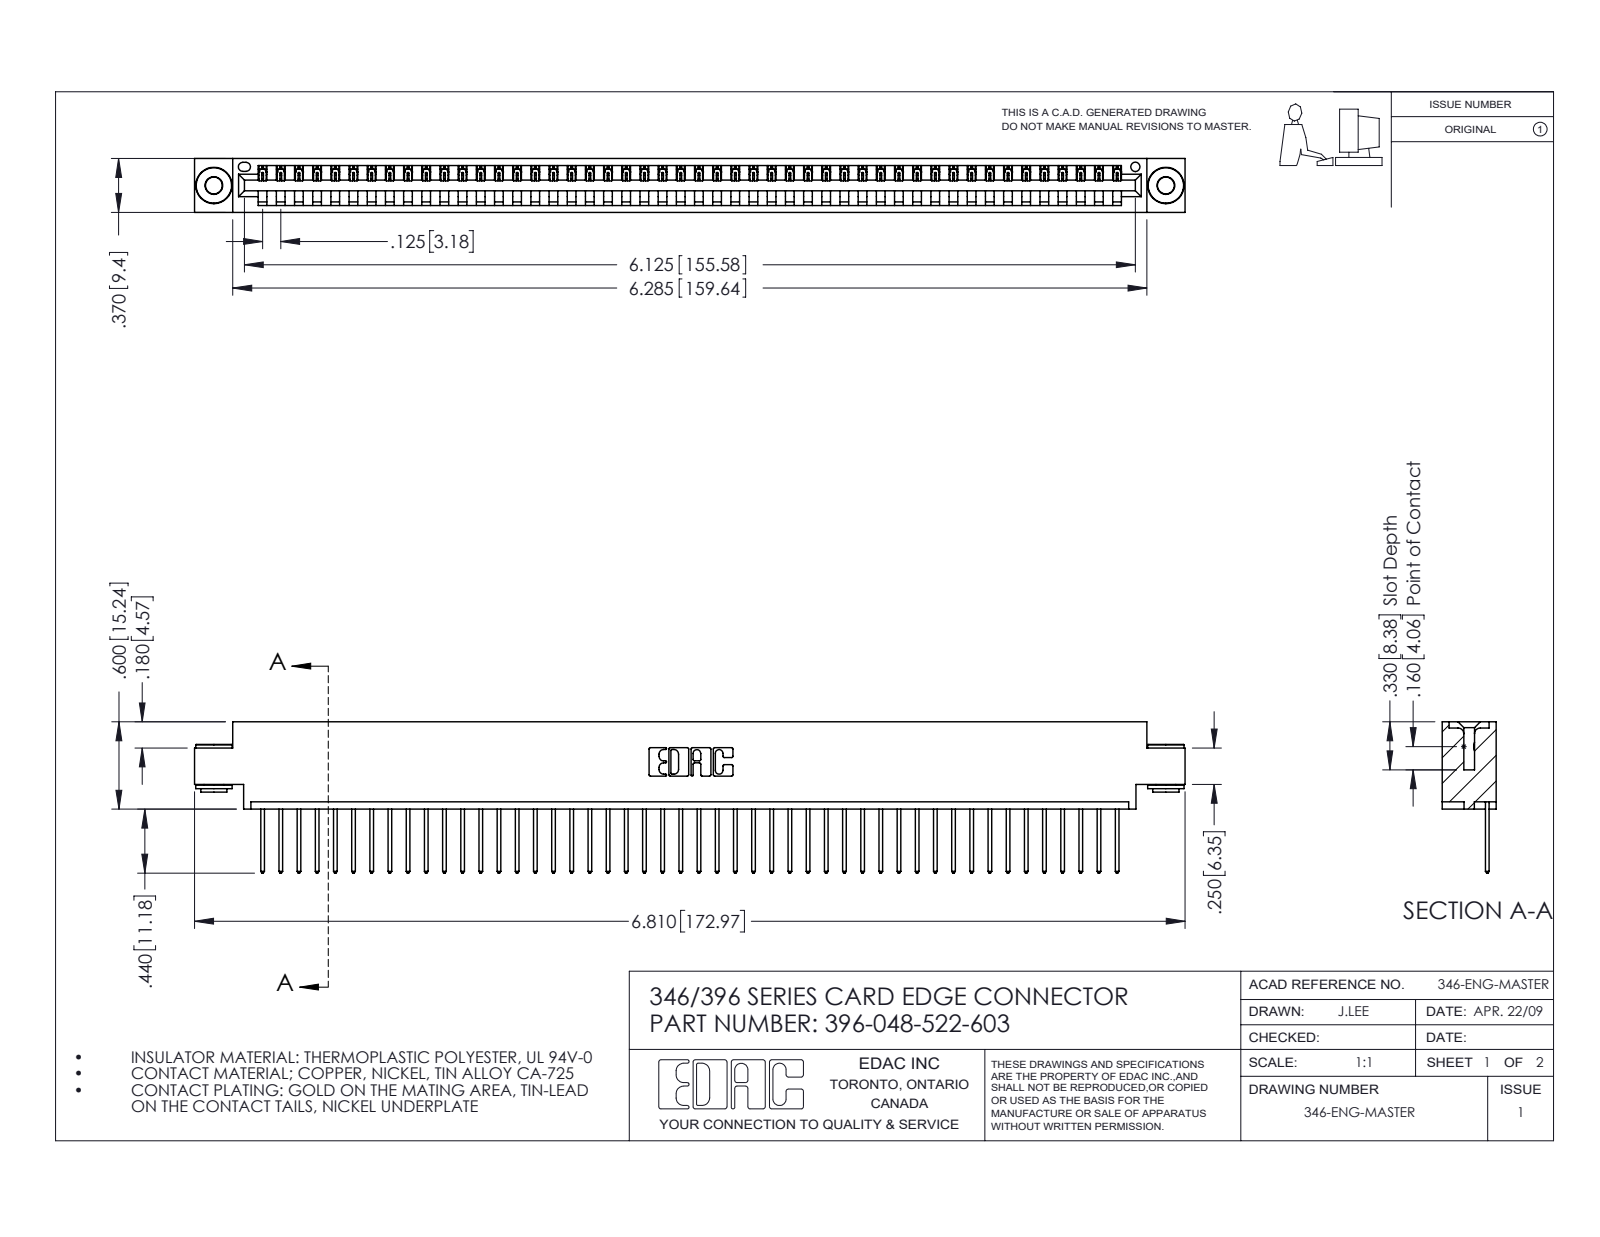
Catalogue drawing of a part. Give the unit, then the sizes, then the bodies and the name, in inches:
Units: inches
Overall size (bounding box): 6.81 × 1.04 × 0.37
Round holes (diameter × count): ⌀0.116 ×2, ⌀0.156 ×2, ⌀0.064 ×1
Round bosses / shafts (diameter × count): ⌀0.25 ×2, ⌀0.18 ×2, ⌀0.136 ×2
Partial cylindrical surfaces — rounded edges, fillets, slot ends (radius × count): R0.006 ×96, R0.01 ×96, R0.01 ×22, R0.007 ×6, R0.031 ×6, R0.026 ×3, R0.031 ×2, R0.04 ×2
Main face-to-face distances: 0.048, 0.322, 0.37, 0.25, 0.025, 0.072, 0.298, 0.148, 0.222, 0.1
Hole centre spacings: 0.246, 6.336, 6.545
Volume: 1.005 in³ · Surface area: 32.87 in²
Bodies: 51 solids, 2948 faces (2010 planar, 930 cylindrical, 8 other)
Part name (STEP PRODUCT): 396-048-522-603; 345-250-002_345-250-002-102; 346 Part_0.170 Offset - 0.156 Dia-TH; 345-292-001_345-293-122
STEP written by: SolidWorks 2016 (CONFIG_CONTROL_DESIGN)
